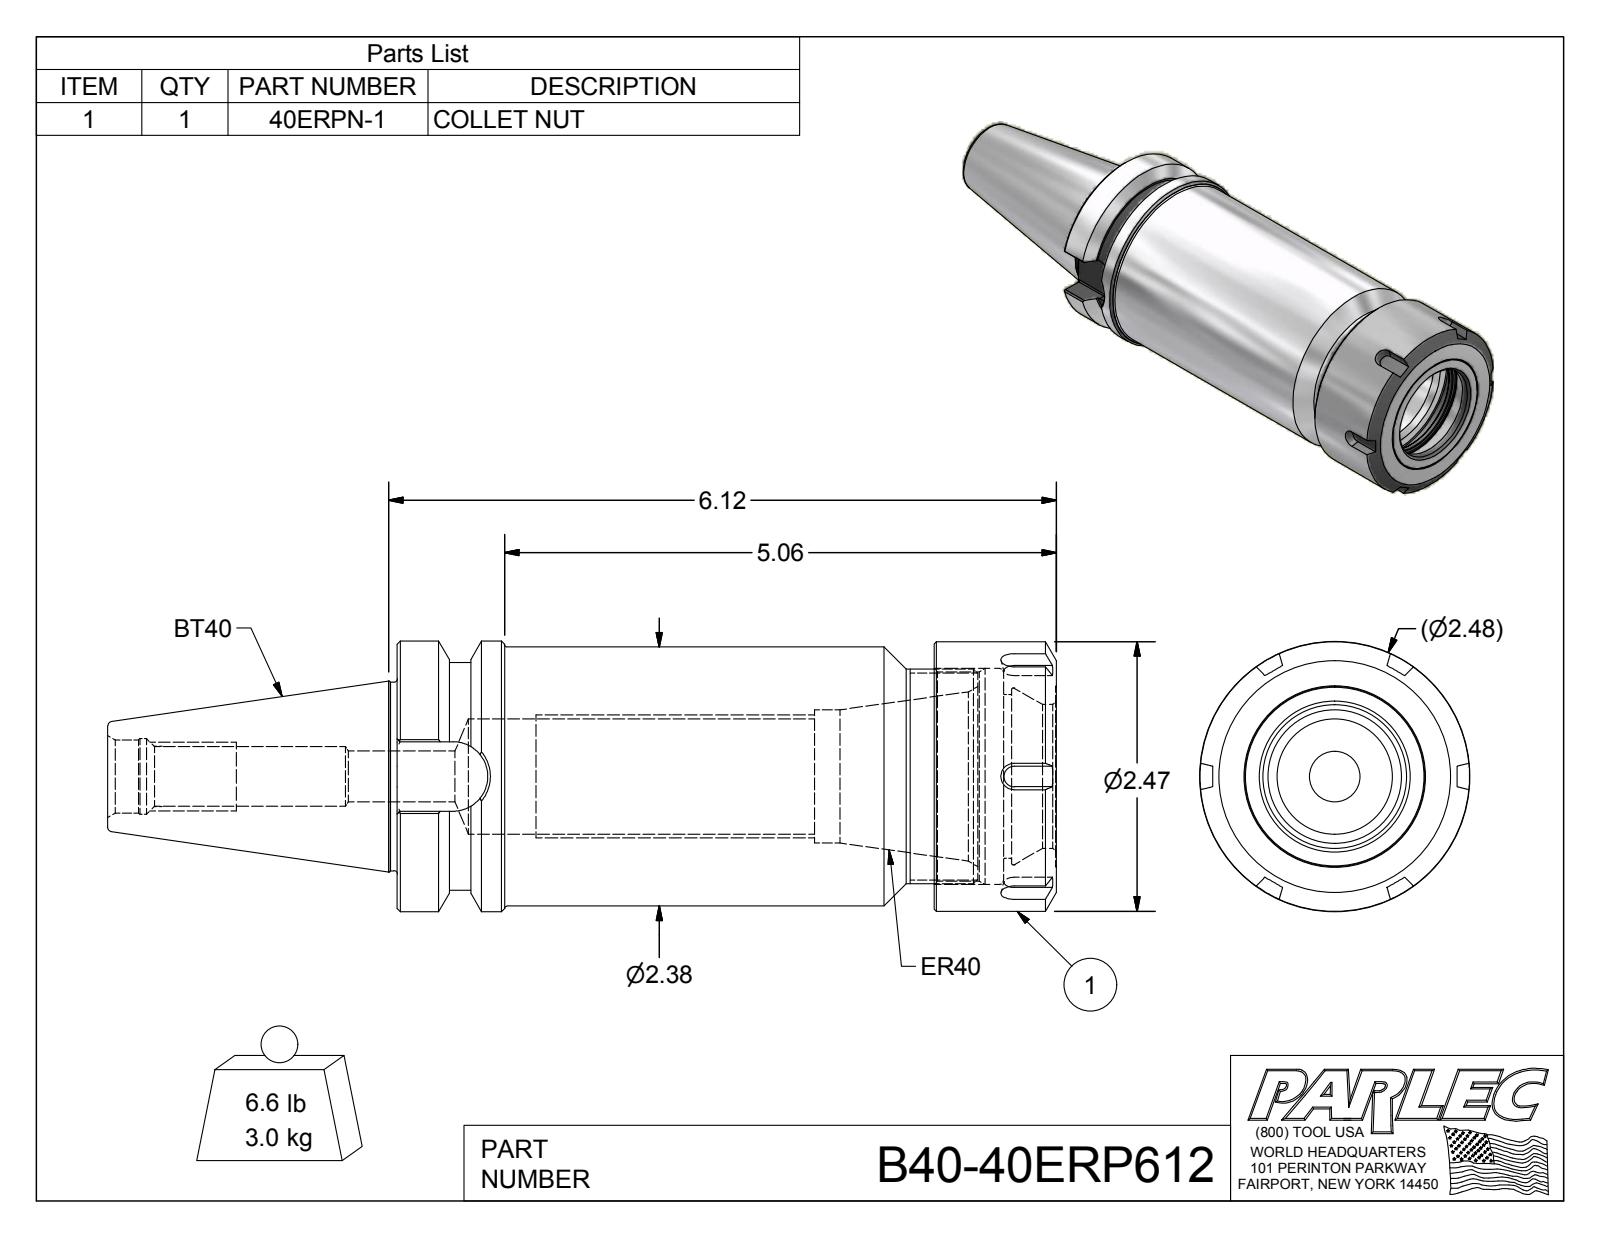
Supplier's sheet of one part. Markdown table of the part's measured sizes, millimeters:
| quantity | value |
| --- | --- |
| part name | B40-40ERP612; B40-40ER6-1; 40ERPN |
| STEP written by | Autodesk Inventor 2012 (AUTOMOTIVE_DESIGN) |
| units | millimeters |
| bodies | 2 solids, 121 faces (47 planar, 30 cylindrical, 44 other) |
| overall size | 220.9 × 63 × 63 |
| volume | 378 700 mm³ |
| surface area | 65 480 mm² |
| round holes (diameter × count) | 11.8 × 1, 13.8 × 1, 17 × 1, 17.6 × 1, 26.8 × 1, 31 × 1, 33.5 × 1, 38.1 × 1, 41.1 × 1, 48.7 × 1, 50.3 × 1 |
| round bosses / shafts (diameter × count) | 63 × 1, 62.7 × 1, 60.3 × 1, 53 × 1, 50 × 1, 43.9 × 1 |
| partial cylindrical surfaces (radius × count) | 0.5 × 8, 8.1 × 1 |
| main face-to-face distances | 153.5, 125, 28.4, 141.2, 16.2, 12.3, 135.2, 10.2, 6, 18.3 |
